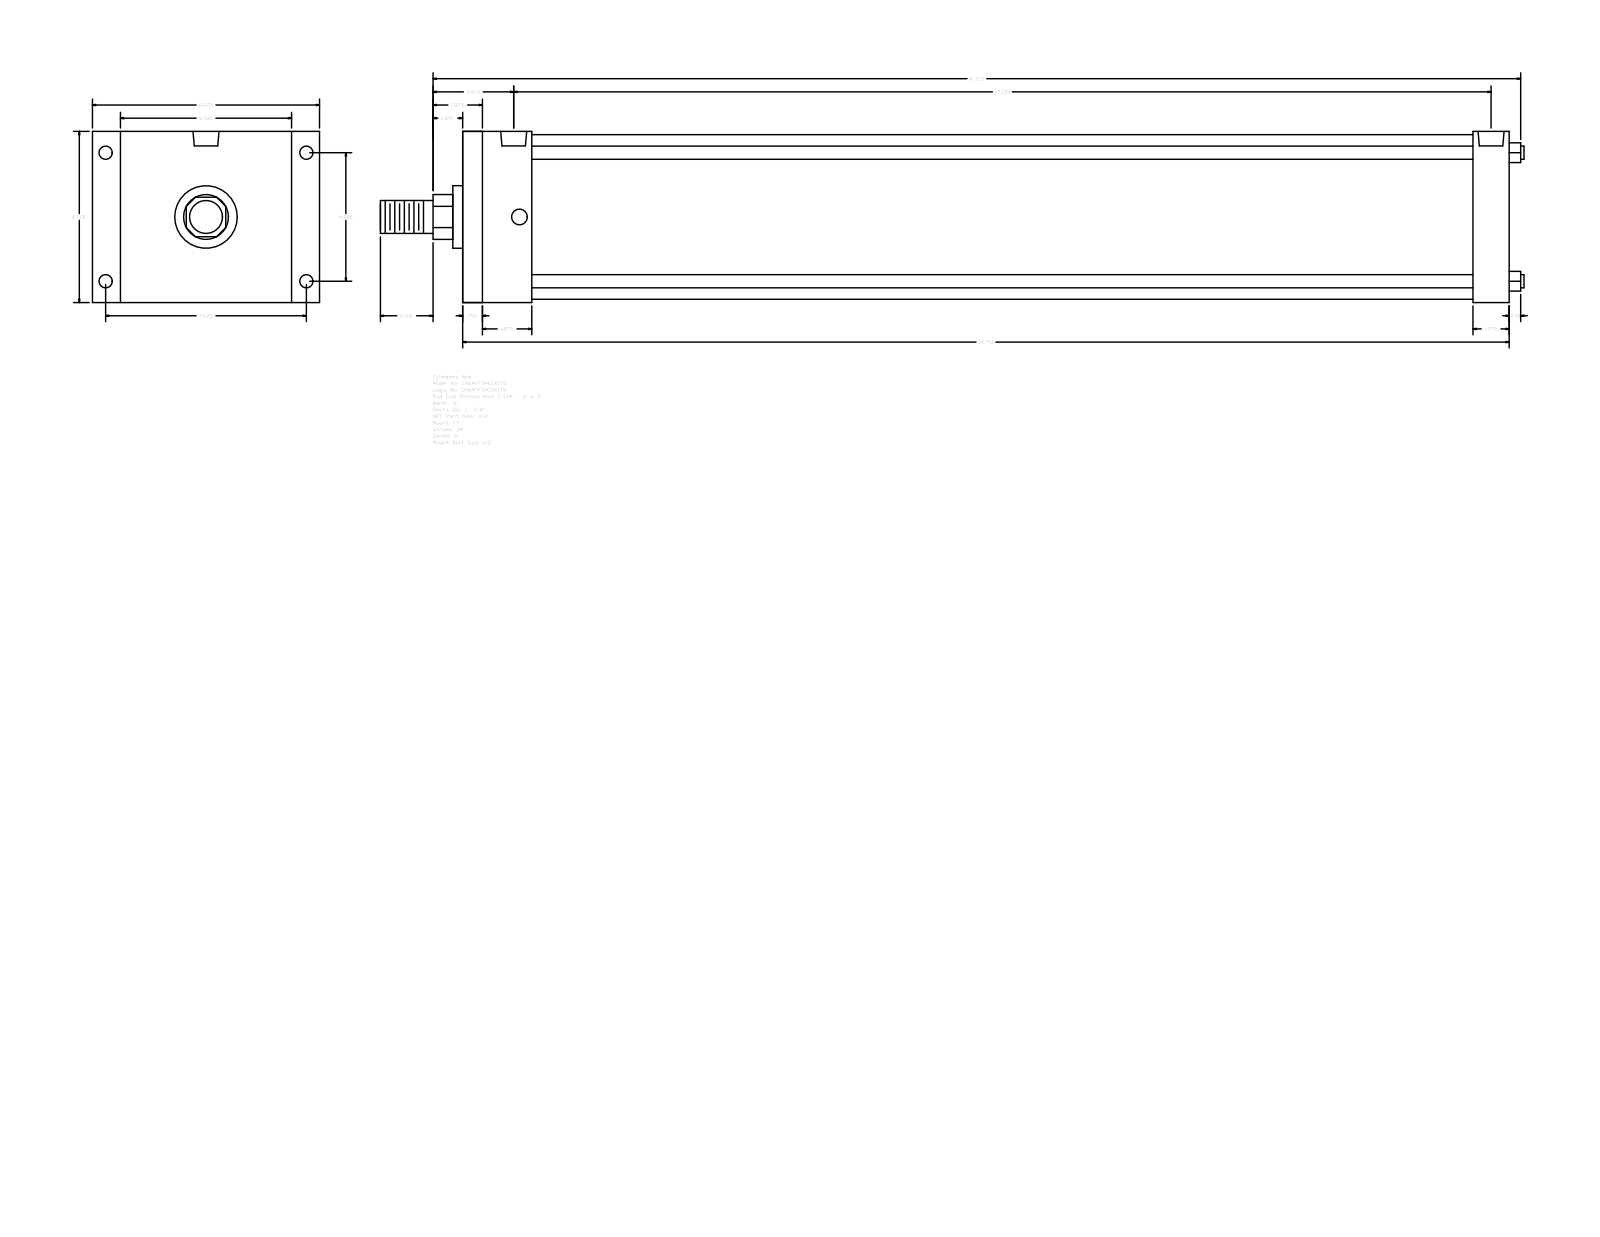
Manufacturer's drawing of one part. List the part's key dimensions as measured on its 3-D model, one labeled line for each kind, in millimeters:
Part name (STEP PRODUCT): A_FF__0600_1.75
STEP written by: GSSL Pune (CONFIG_CONTROL_DESIGN)
Units: millimetres
Bodies: 0 solids, 92 faces (64 planar, 28 cylindrical, 0 other)
Overall size (bounding box): 1103.31 × 219.07 × 165.1
Round holes (diameter × count): ⌀12.7 ×4, ⌀15.08 ×4, ⌀25.12 ×2
Round bosses / shafts (diameter × count): ⌀12.7 ×4, ⌀158.75 ×1, ⌀60.33 ×1, ⌀44.45 ×1, ⌀31.75 ×1
Partial cylindrical surfaces — rounded edges, fillets, slot ends (radius × count): R21.63 ×1
Main face-to-face distances: 165.1, 1009.65, 19.05, 990.6, 66.68, 47.63, 942.97, 974.73, 955.68, 908.05
Hole centre spacings: 5.56, 123.96, 193.68, 229.95, 931.85, 937.41, 942.97
